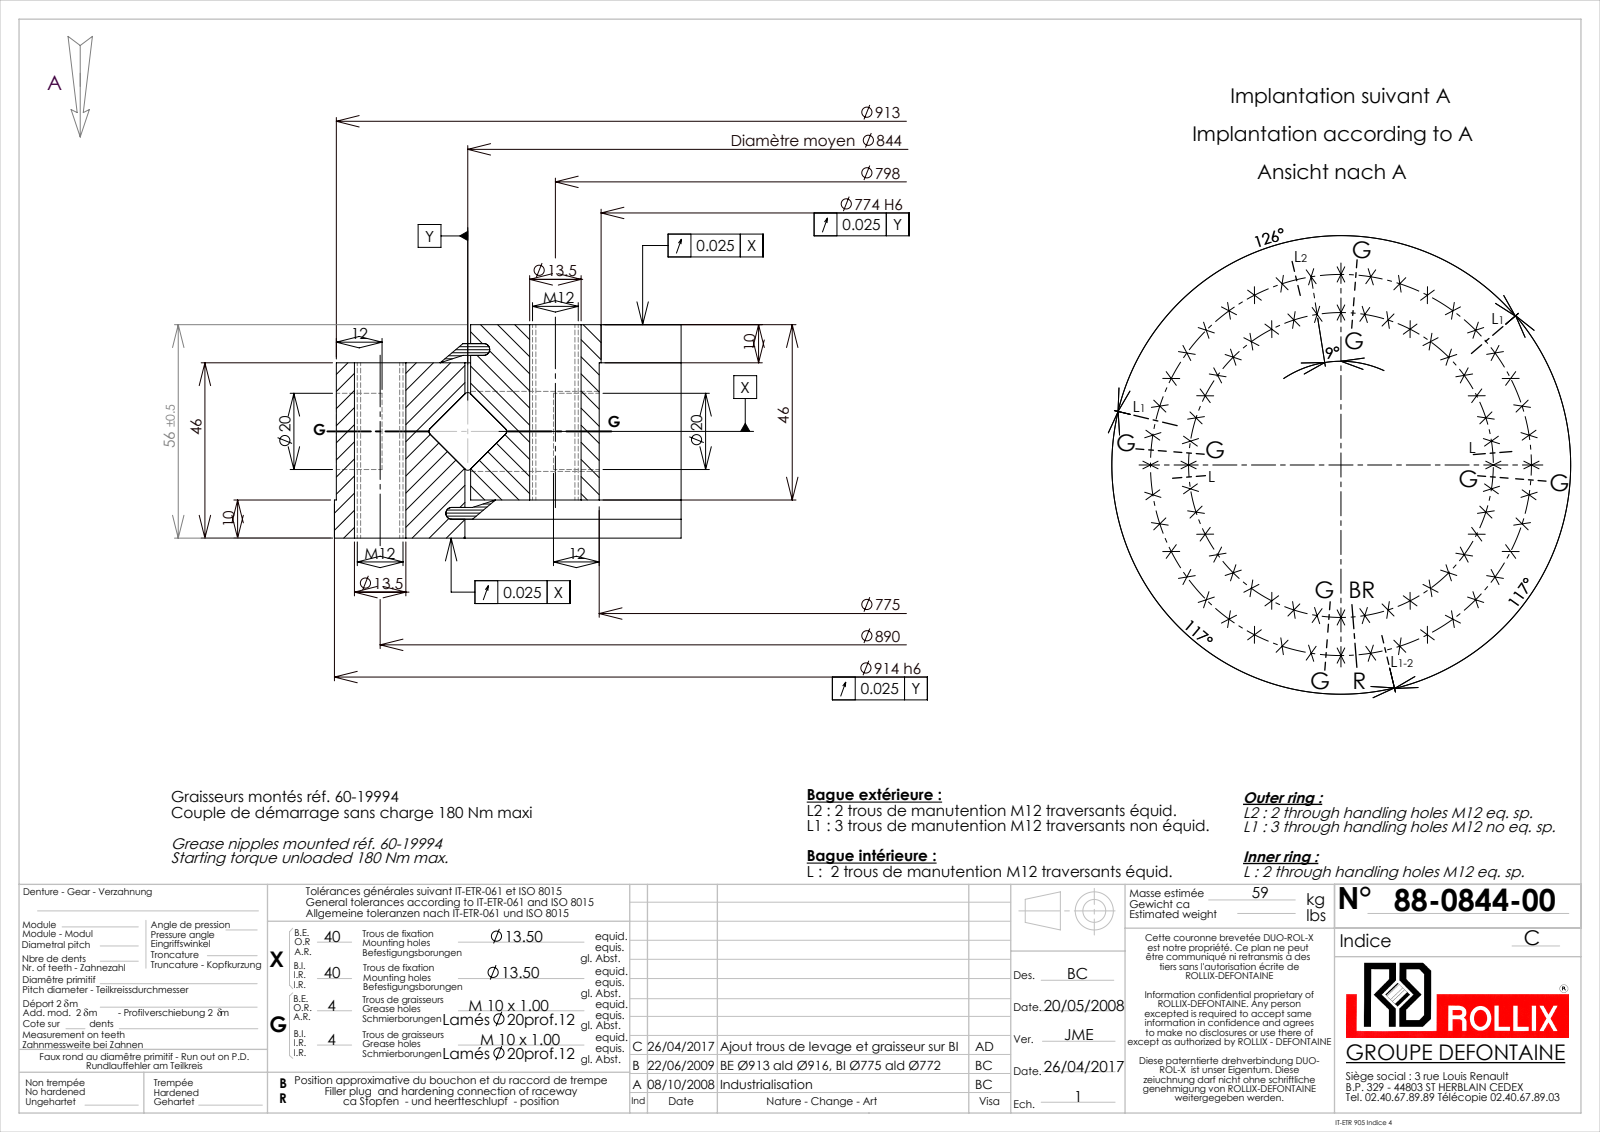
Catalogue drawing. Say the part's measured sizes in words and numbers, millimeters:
The part is named "88-0844-00". Its 3-D file was written by "SolidWorks 2016 (CONFIG_CONTROL_DESIGN)". It is 13 solids with 479 faces: 104 planar, 246 cylindrical and 129 other. Overall it measures 914 by 914 by 56 millimeters. Its volume is 7 251 000 cubic millimeters and its surface area 1 252 000 square millimeters. Round holes: 80 of diameter 13.5, 8 of diameter 9, 8 of diameter 20, 6 of diameter 10.2, 1 of diameter 774, 1 of diameter 775, 1 of diameter 845.5, 1 of diameter 855.5. Round bosses or shafts: 4 of diameter 10, 1 of diameter 914, 1 of diameter 913, 1 of diameter 842.5, 1 of diameter 832.5, 1 of diameter 15. The main face-to-face distances are 46, 10, 36, 56, 4.95, 51.05, 5.05, 41.05, 8.05, 47.95. The hole center spacings are 445, 69.83, 207.77, 404.05, 340.59, 465.02, 523.13, 275.03.
